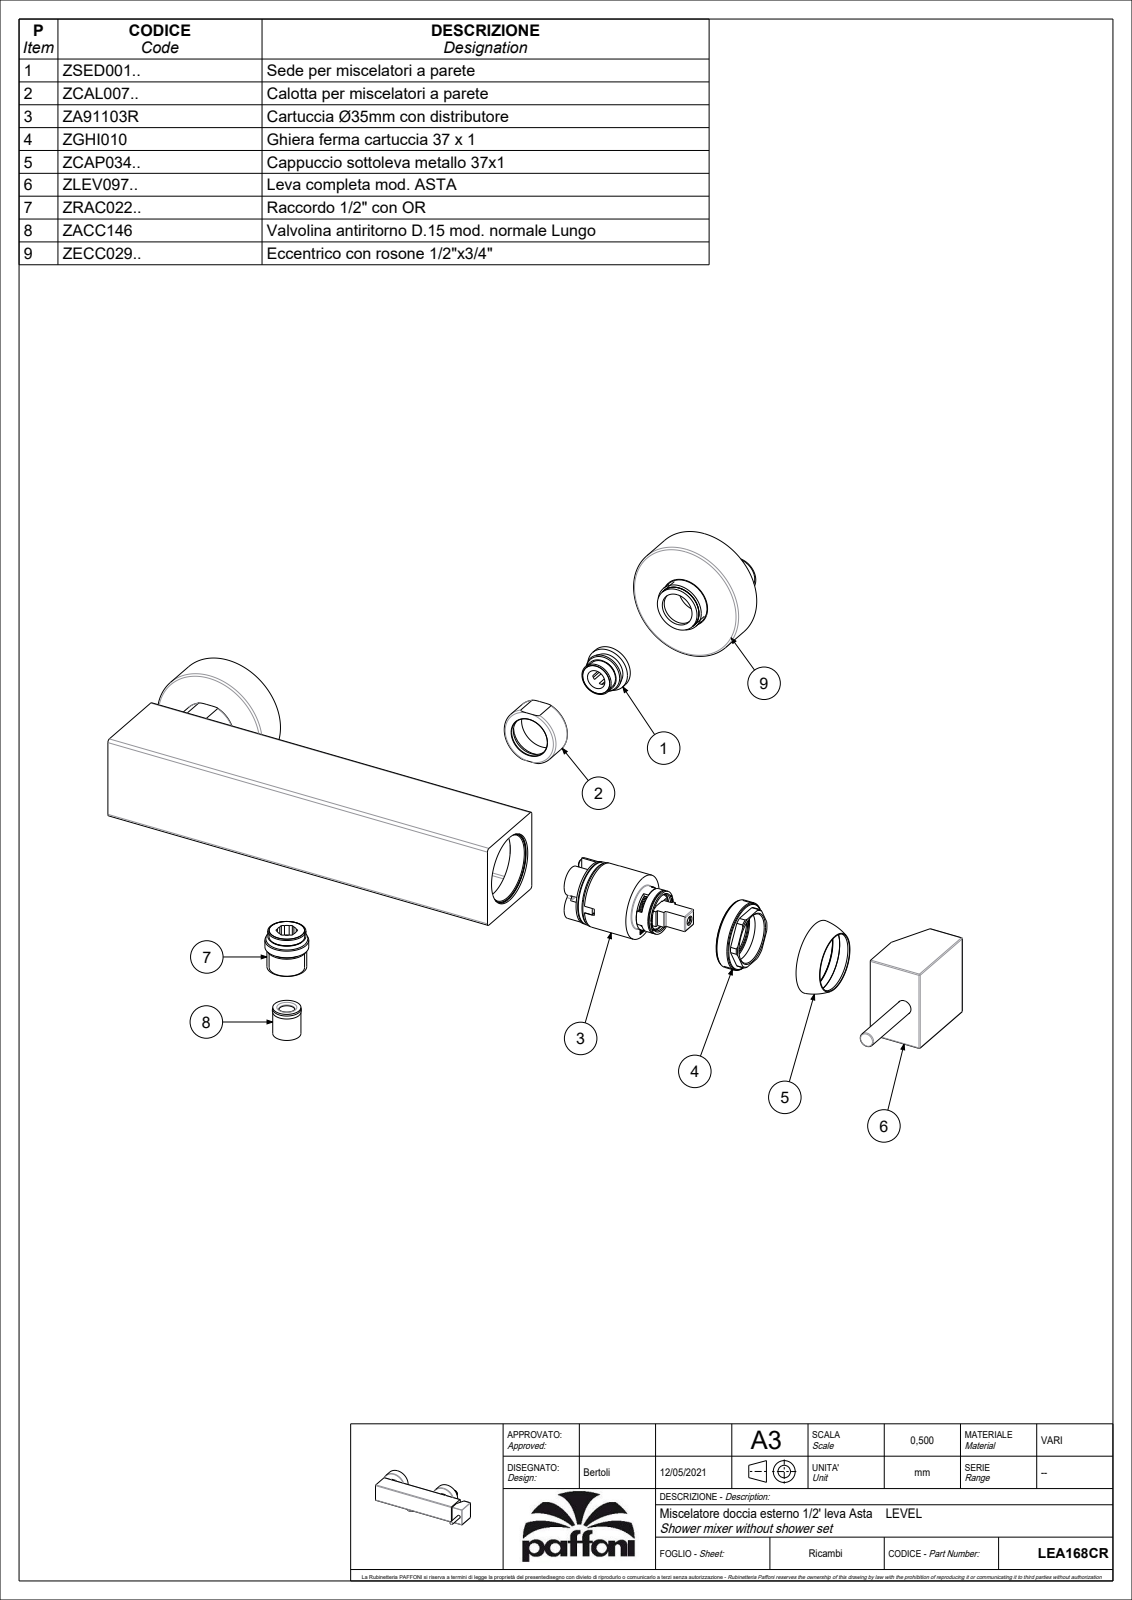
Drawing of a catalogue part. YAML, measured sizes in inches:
part_name: "LEA168CR"
step_written_by: "CREO PARAMETRIC BY PTC INC, 2020044 (CONFIG_CONTROL_DESIGN)"
units: inches
bodies: {solids: 1, faces: 1555, planar: 767, cylindrical: 459, other: 329}
overall_size: [10.758, 4.754, 2.618]
volume: 15.69
surface_area: 264.8
round_holes:
  - {diameter: 0.472, count: 4}
  - {diameter: 0.354, count: 3}
  - {diameter: 0.157, count: 2}
  - {diameter: 0.276, count: 2}
  - {diameter: 0.315, count: 2}
  - {diameter: 0.413, count: 2}
  - {diameter: 0.709, count: 2}
  - {diameter: 0.85, count: 2}
  - {diameter: 0.965, count: 2}
  - {diameter: 0.984, count: 2}
  - {diameter: 1.457, count: 2}
  - {diameter: 2.453, count: 2}
round_bosses_or_shafts:
  - {diameter: 2.5, count: 2}
  - {diameter: 1.063, count: 2}
  - {diameter: 0.945, count: 2}
  - {diameter: 0.697, count: 2}
  - {diameter: 1.378, count: 1}
  - {diameter: 1.37, count: 1}
  - {diameter: 1.331, count: 1}
  - {diameter: 1.268, count: 1}
partial_cylinders:
  - {radius: 0.039, count: 90}
  - {radius: 0.02, count: 54}
  - {radius: 0.006, count: 11}
  - {radius: 0.012, count: 9}
  - {radius: 0.059, count: 4}
  - {radius: 0.276, count: 4}
  - {radius: 0.177, count: 2}
  - {radius: 0.197, count: 2}
face_to_face_distances: [0.148, 1.683, 1.831, 1.535, 0.118, 0.591, 0.738, 2.421, 2.274, 1.654]
hole_center_spacings: [0.028, 0.335, 0.339, 0.513, 0.52, 0.532, 0.236, 0.512]
